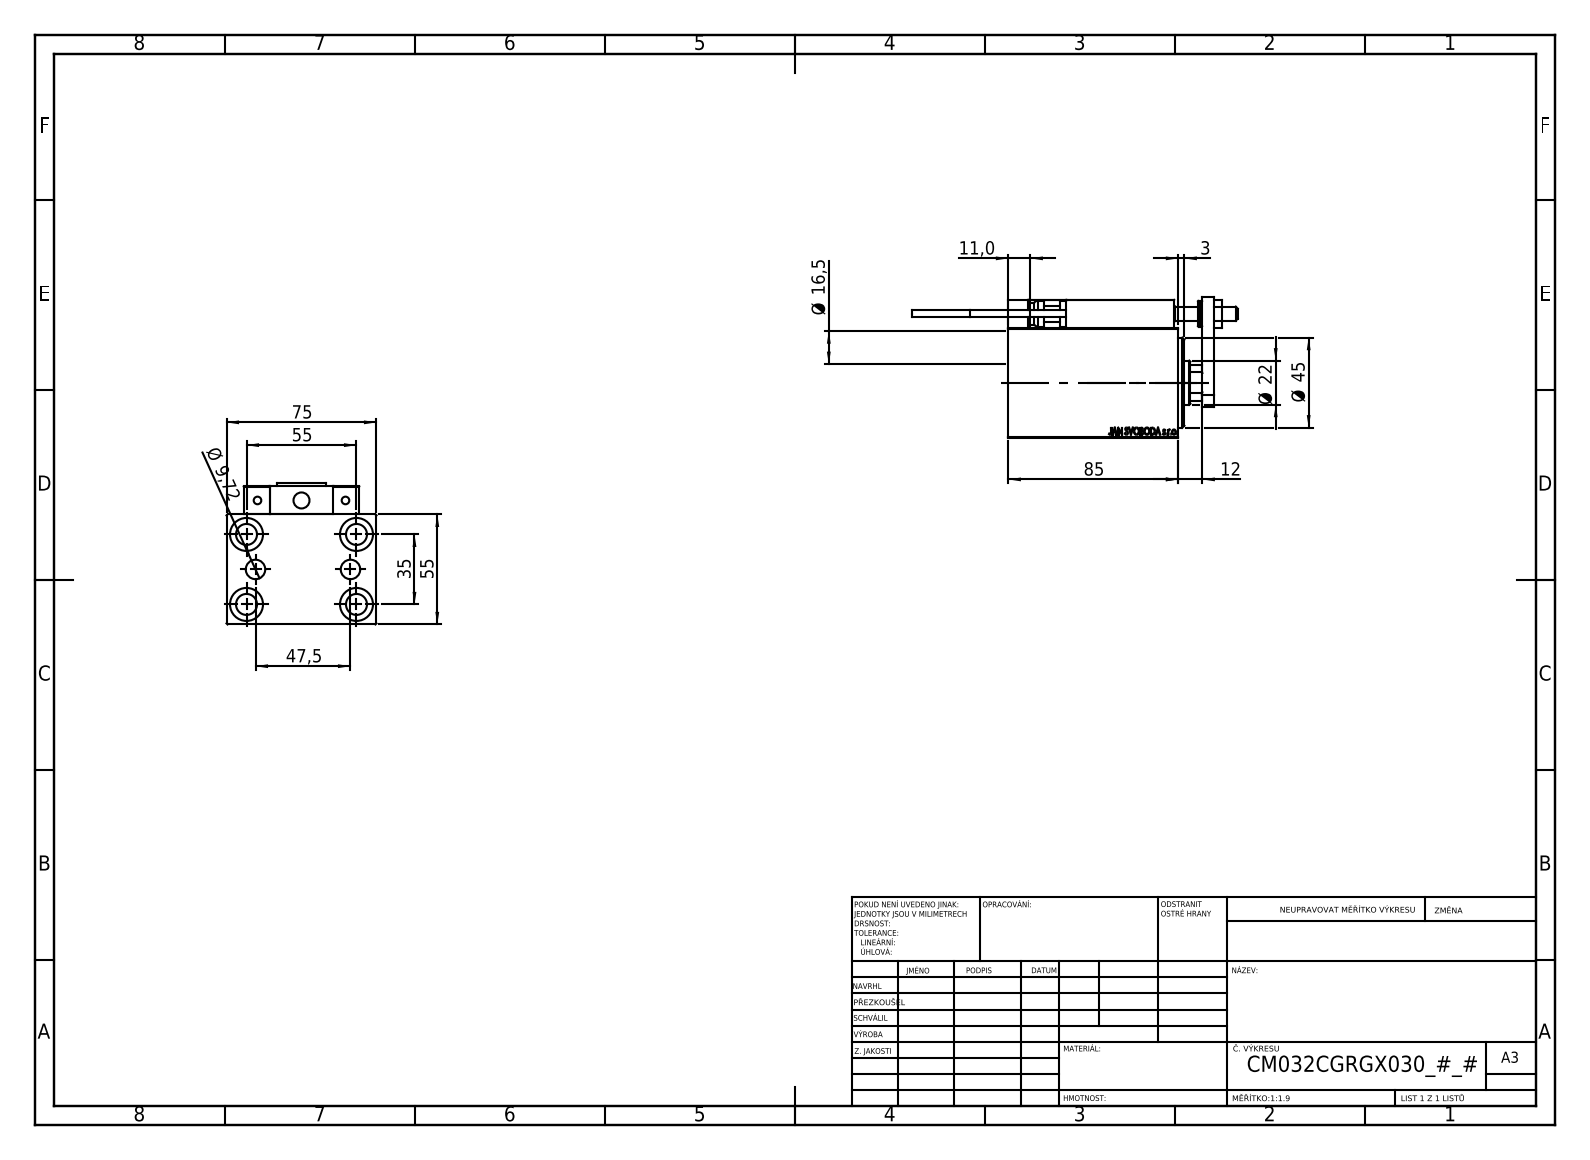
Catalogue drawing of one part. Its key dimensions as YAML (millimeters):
part_name: "ALLEN BOLT D8; SWITCH DIM B,W; V450CM_VC_B; KONCOVKA (+7 more)"
step_written_by: "SolidWorks 2019 (CONFIG_CONTROL_DESIGN)"
units: millimeters
bodies: {solids: 23, faces: 1272, planar: 558, cylindrical: 180, other: 534}
overall_size: [162.7, 75, 70.5]
volume: 349554
surface_area: 89720
round_holes:
  - {diameter: 8, count: 5}
  - {diameter: 10.5, count: 5}
  - {diameter: 16.5, count: 5}
  - {diameter: 3.2, count: 4}
  - {diameter: 4, count: 4}
  - {diameter: 5, count: 2}
  - {diameter: 9.72, count: 2}
  - {diameter: 7, count: 1}
  - {diameter: 22, count: 1}
  - {diameter: 25.5, count: 1}
  - {diameter: 32, count: 1}
  - {diameter: 34, count: 1}
round_bosses_or_shafts:
  - {diameter: 5, count: 2}
  - {diameter: 3.8, count: 2}
  - {diameter: 13, count: 1}
  - {diameter: 11, count: 1}
partial_cylinders:
  - {radius: 0.3, count: 30}
  - {radius: 3, count: 2}
  - {radius: 10.5, count: 1}
face_to_face_distances: [55, 75, 14, 10, 69, 12, 7, 25, 15, 18]
hole_center_spacings: [32.6, 11.37, 17.76, 18.07, 20, 29.59, 29.69, 32.33]
